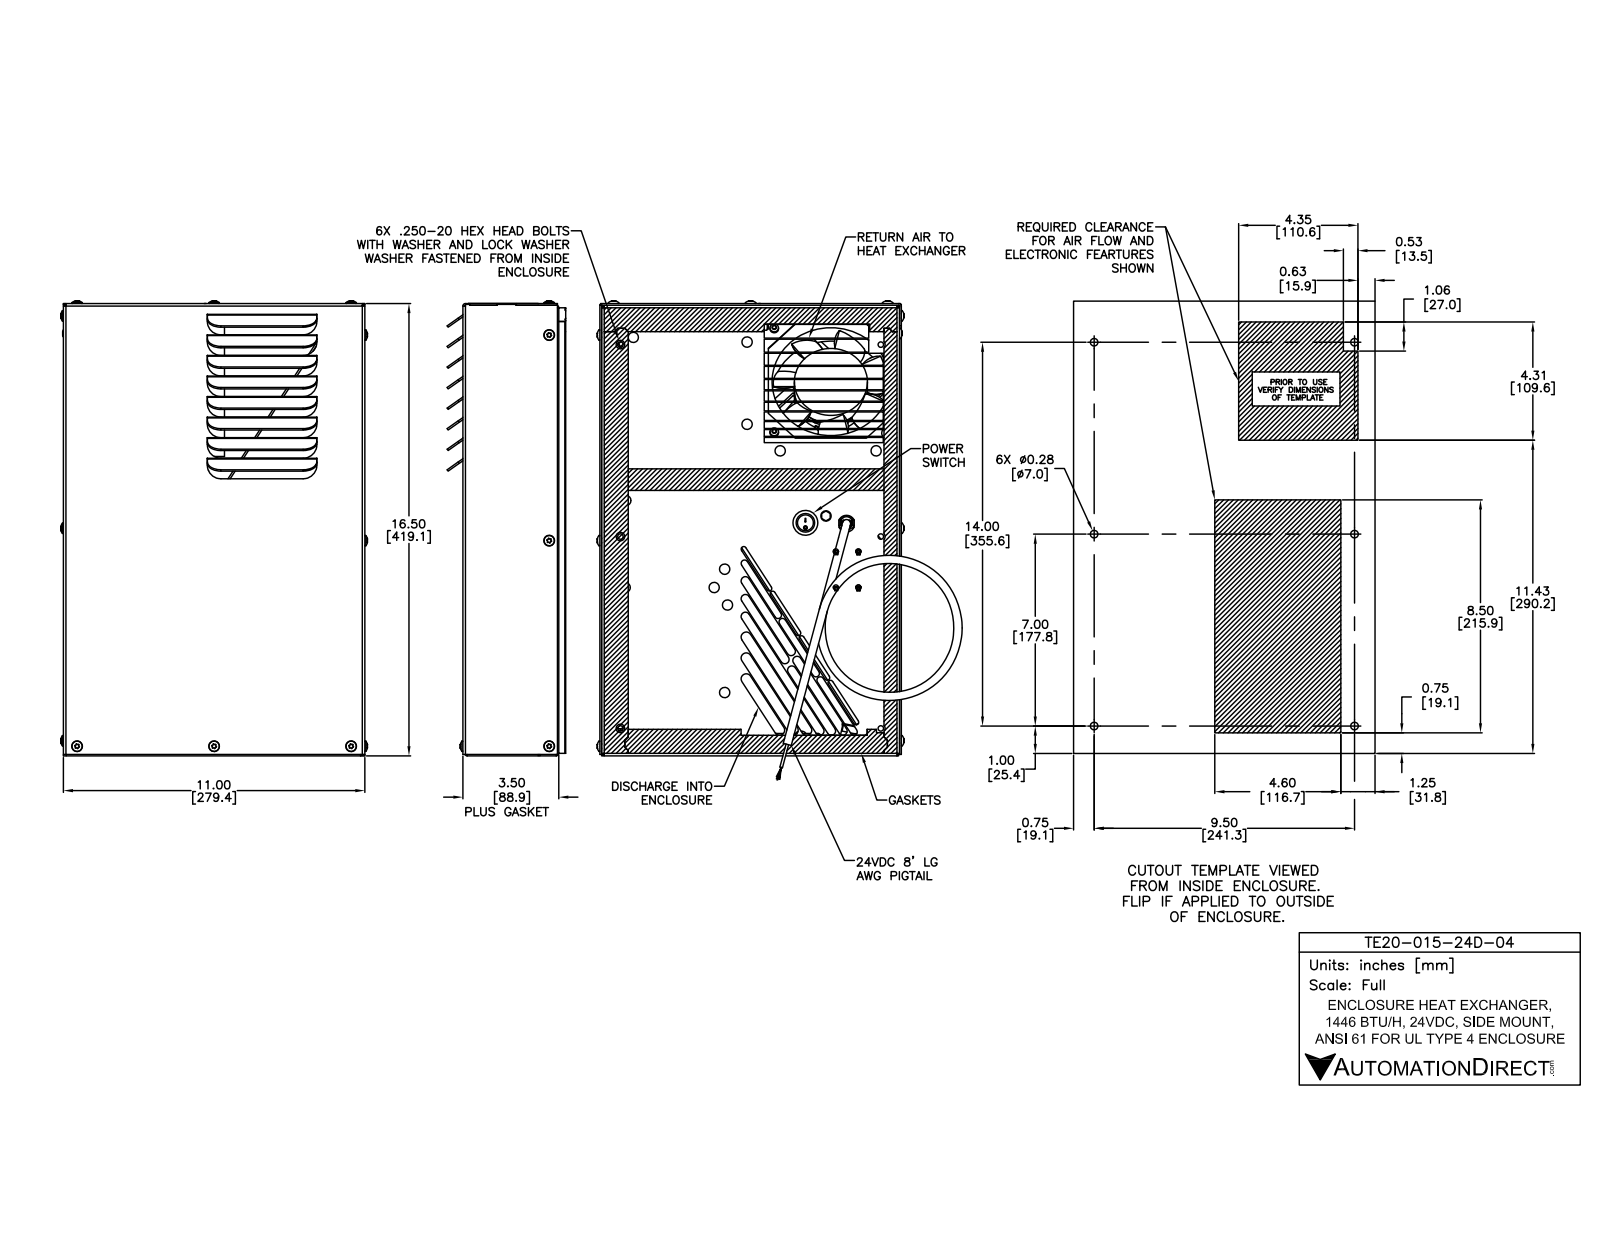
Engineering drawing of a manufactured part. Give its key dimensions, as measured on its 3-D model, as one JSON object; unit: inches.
{"part_name": "TE20-015-24D-04", "step_written_by": "SolidWorks 2017 (AUTOMOTIVE_DESIGN)", "units": "inches", "bodies": {"solids": 66, "faces": 2808, "planar": 1639, "cylindrical": 897, "other": 272}, "overall_size": [17.697, 13.352, 7.523], "volume_in3": 139.3, "surface_area_in2": 2393, "round_holes": [[0.193, 21], [0.219, 20], [0.203, 11], [0.138, 8], [0.163, 8], [0.177, 8], [0.5, 8], [0.109, 6], [0.201, 6], [0.159, 4], [0.213, 4], [0.312, 3]], "round_bosses_or_shafts": [[0.366, 13], [0.17, 13], [0.313, 8], [0.31, 8], [0.187, 8], [0.164, 8], [0.129, 8], [0.325, 6]], "partial_cylinders_radius": [[0.019, 79], [0.019, 78], [0.031, 54], [0.093, 48], [0.024, 38], [0.06, 28], [0.03, 18], [0.025, 16]], "face_to_face_distances": [0.062, 3.438, 0.062, 3.376, 3.5, 10.871, 10.933, 0.25, 0.067, 3.75], "hole_center_spacings": [4.134, 1.25, 5.846, 2.923, 5.846, 4.134, 2.923, 1.125]}
